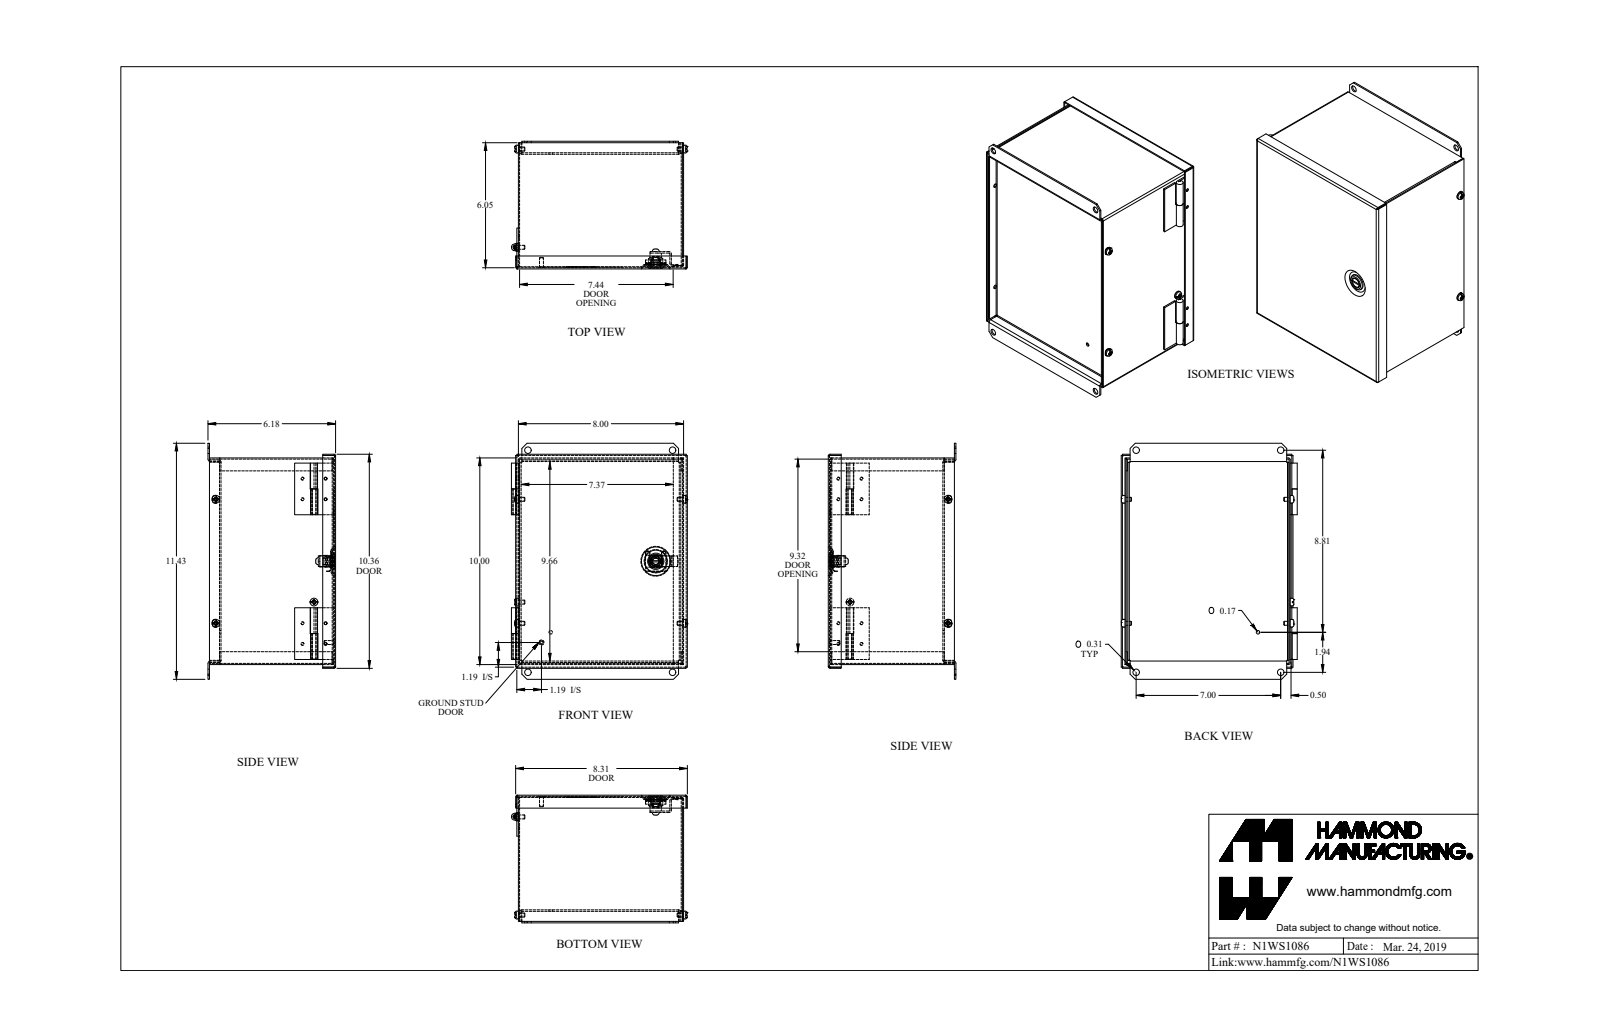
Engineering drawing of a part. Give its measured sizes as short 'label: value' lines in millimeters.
name: N1WS1086
written by: SolidWorks 2018 (AUTOMOTIVE_DESIGN)
unit: mm
bodies: 15 solids, 539 faces (290 planar, 196 cylindrical, 53 other)
size: 290.2 × 216.4 × 156.9
volume: 455 400 mm³; area: 592 800 mm²
holes: 8× ⌀3.6, 4× ⌀4.3, 4× ⌀7.9, 1× ⌀4.7, 1× ⌀8.1, 1× ⌀12.1
bosses: 8× ⌀3.3, 3× ⌀9.5, 3× ⌀4.8, 1× ⌀20, 1× ⌀13.9, 1× ⌀12, 1× ⌀11.9, 1× ⌀9.3
rounds: 9× R0.7, 9× R2.2, 8× R0.9, 6× R2.7, 4× R0.3, 4× R2.5, 4× R2.8, 2× R2
face distances: 1.4, 201.8, 1.8, 252.6, 1.4, 141.3, 142.8, 139.5, 140.9, 203.2
hole spacings: 177.8, 25.4, 28.4, 38.1, 180.1, 152.4, 106.6, 109.6
